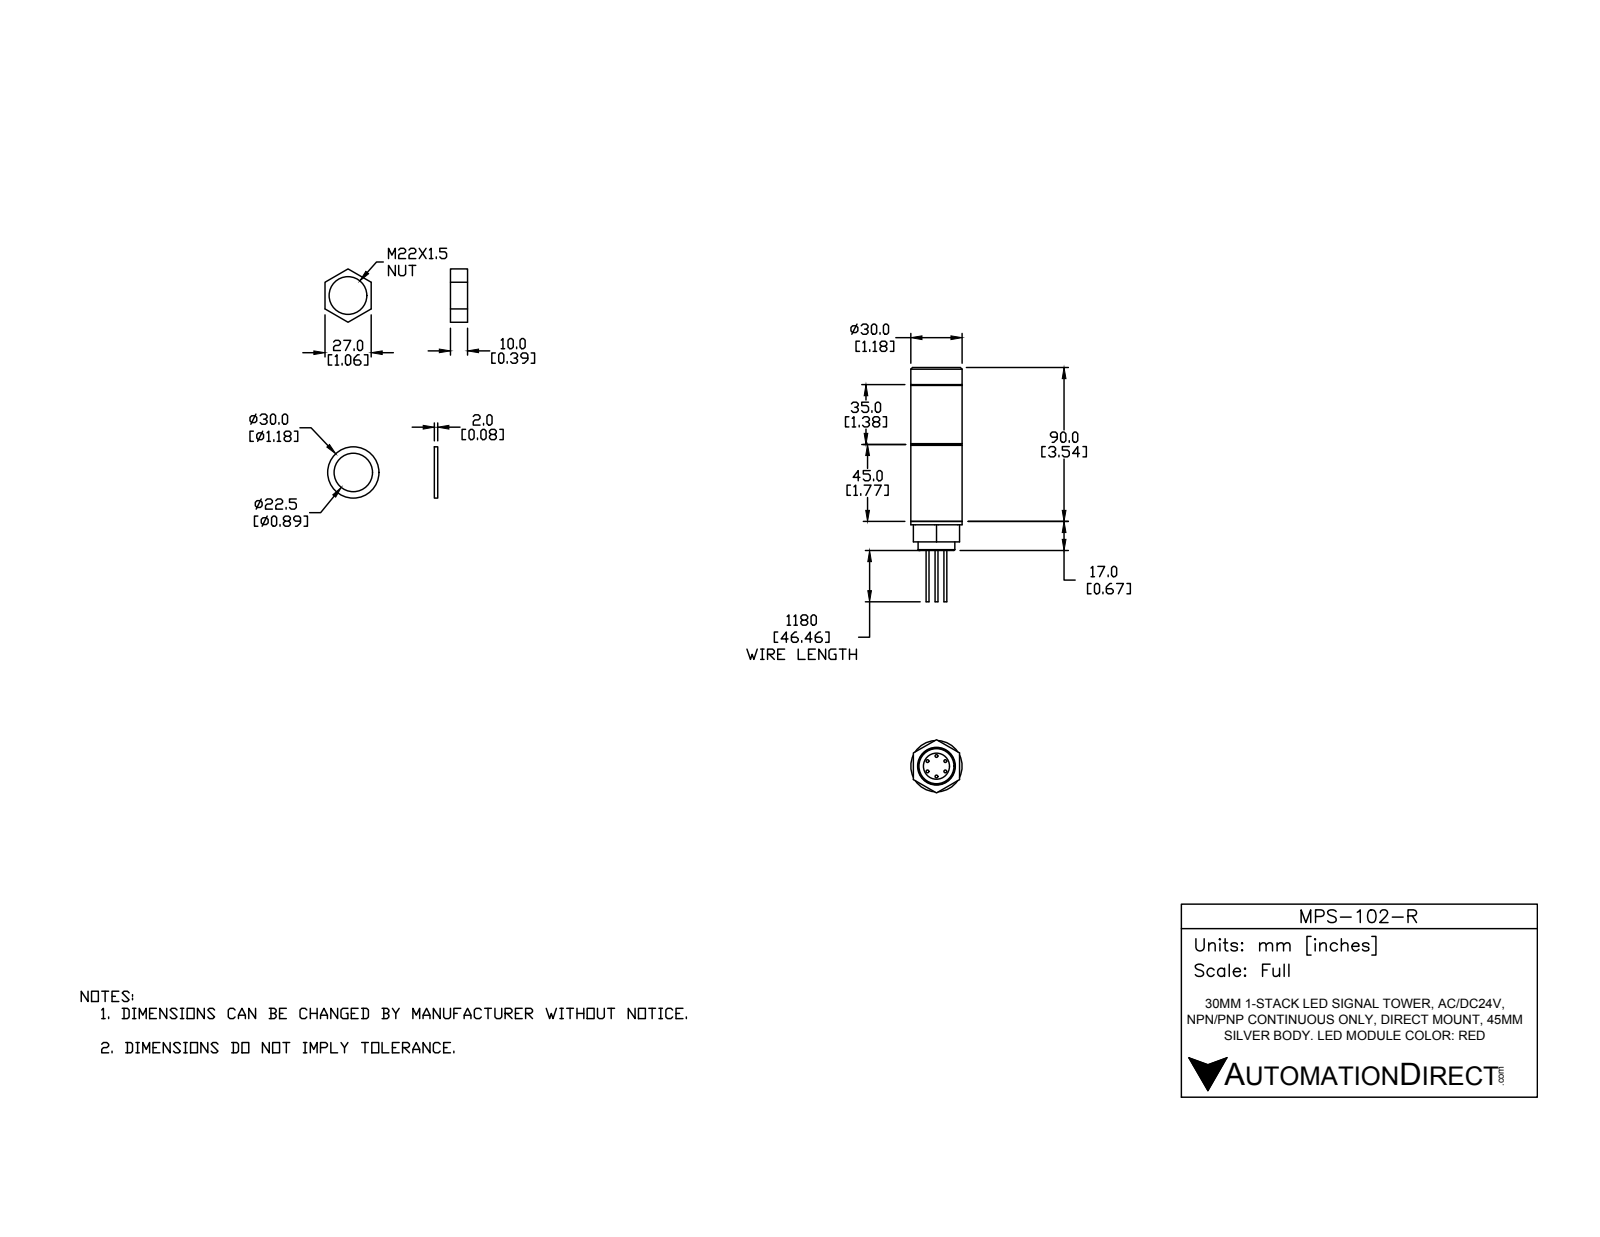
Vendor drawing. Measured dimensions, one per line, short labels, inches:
name: MPS-102-R
written by: SolidWorks 2016 (AUTOMOTIVE_DESIGN)
unit: in
bodies: 12 solids, 95 faces (47 planar, 36 cylindrical, 12 other)
size: 5.394 × 1.228 × 1.181
volume: 3.635 in³; area: 35.49 in²
holes: 1× ⌀0.126, 1× ⌀0.303, 1× ⌀0.602, 1× ⌀0.815, 1× ⌀0.866
bosses: 6× ⌀0.067, 1× ⌀1.181, 1× ⌀0.846, 1× ⌀0.197
face distances: 1.378, 1.772, 1.85, 3.15, 3.622, 0.394, 0.472, 2.244, 0.079, 3.228
